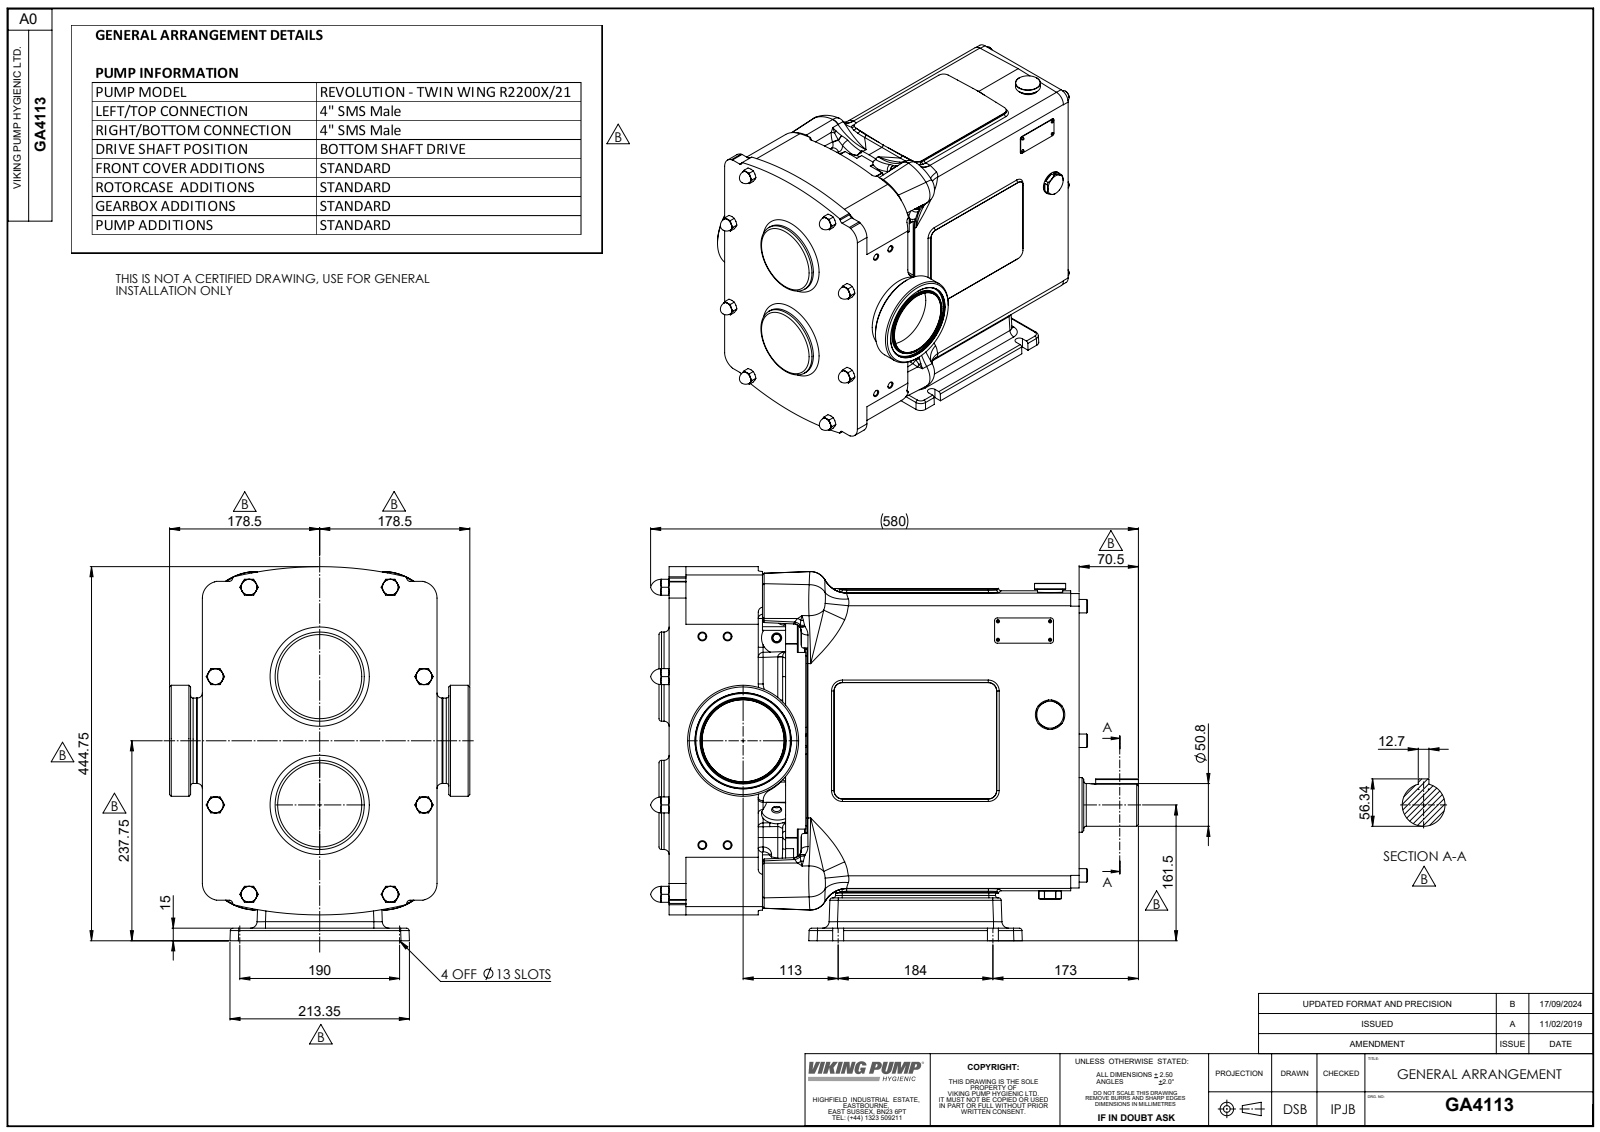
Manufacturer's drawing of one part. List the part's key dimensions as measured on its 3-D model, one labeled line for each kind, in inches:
Part name (STEP PRODUCT): Copy of Z94-5101-66 - 4 INCH SMS1145^GA4113; Copy of R2200 CPP H BSD^GA4113; GA4113
STEP written by: SolidWorks 2023 (AUTOMOTIVE_DESIGN)
Units: inches
Bodies: 4 solids, 1713 faces (531 planar, 413 cylindrical, 769 other)
Overall size (bounding box): 22.835 × 17.51 × 14.055
Volume: 2 403 in³ · Surface area: 1 973 in²
Round holes (diameter × count): ⌀0.335 ×4, ⌀5.866 ×2, ⌀1.378 ×1, ⌀3.839 ×1, ⌀4.488 ×1
Round bosses / shafts (diameter × count): ⌀0.551 ×10, ⌀0.315 ×10, ⌀0.63 ×6, ⌀0.709 ×4, ⌀7.362 ×2, ⌀5.512 ×2, ⌀4.173 ×2, ⌀1.24 ×2
Partial cylindrical surfaces — rounded edges, fillets, slot ends (radius × count): R0.236 ×48, R0.118 ×44, R0.394 ×28, R0.008 ×24, R0.039 ×16, R0.197 ×16, R0.315 ×10, R0.591 ×8
Main face-to-face distances: 7.48, 19.193, 0.118, 7.598, 13.74, 5.453, 1.634, 1.752, 9.232, 9.35
Hole centre spacings: 1.181, 4.936, 5.242, 9.764, 9.835, 6.004
